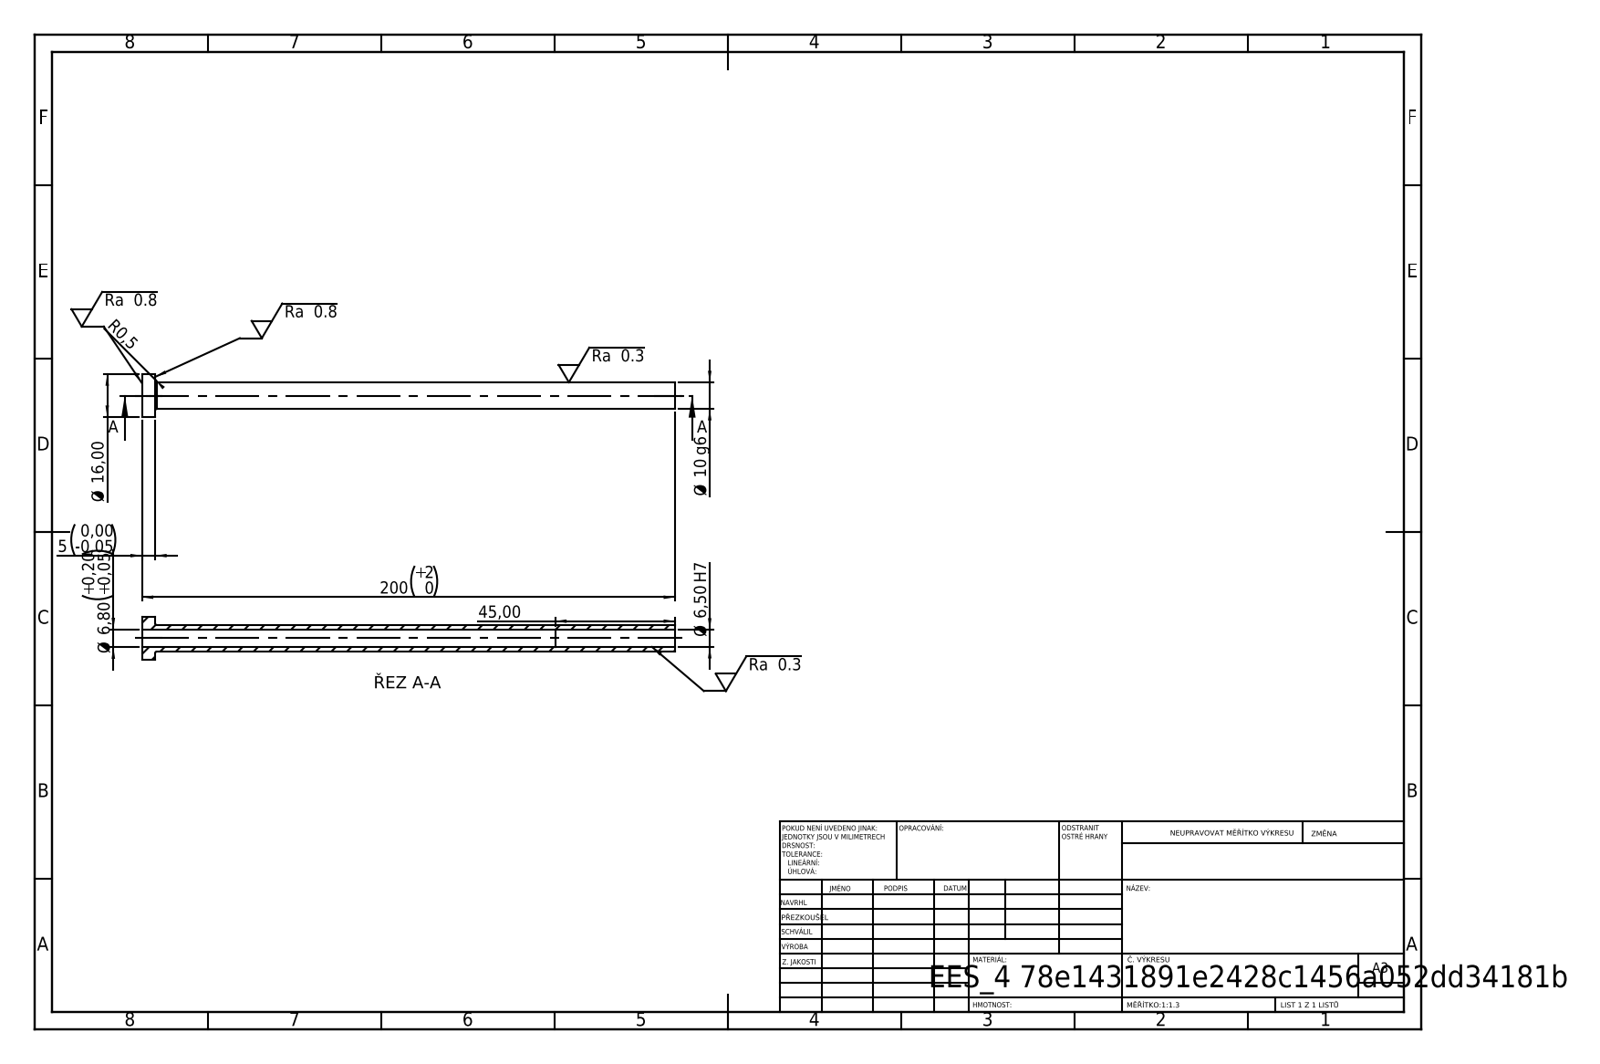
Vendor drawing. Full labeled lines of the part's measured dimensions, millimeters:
STEP written by: SolidWorks 2019 (CONFIG_CONTROL_DESIGN)
Units: millimetres
Bodies: 1 solid, 14 faces (4 planar, 8 cylindrical, 2 other)
Overall size (bounding box): 200 × 16 × 16
Volume: 9 200 mm³ · Surface area: 10 937 mm²
Round holes (diameter × count): ⌀6.5 ×1, ⌀6.8 ×1
Round bosses / shafts (diameter × count): ⌀16 ×1, ⌀10 ×1
Main face-to-face distances: 5, 200, 195, 155, 150, 45
